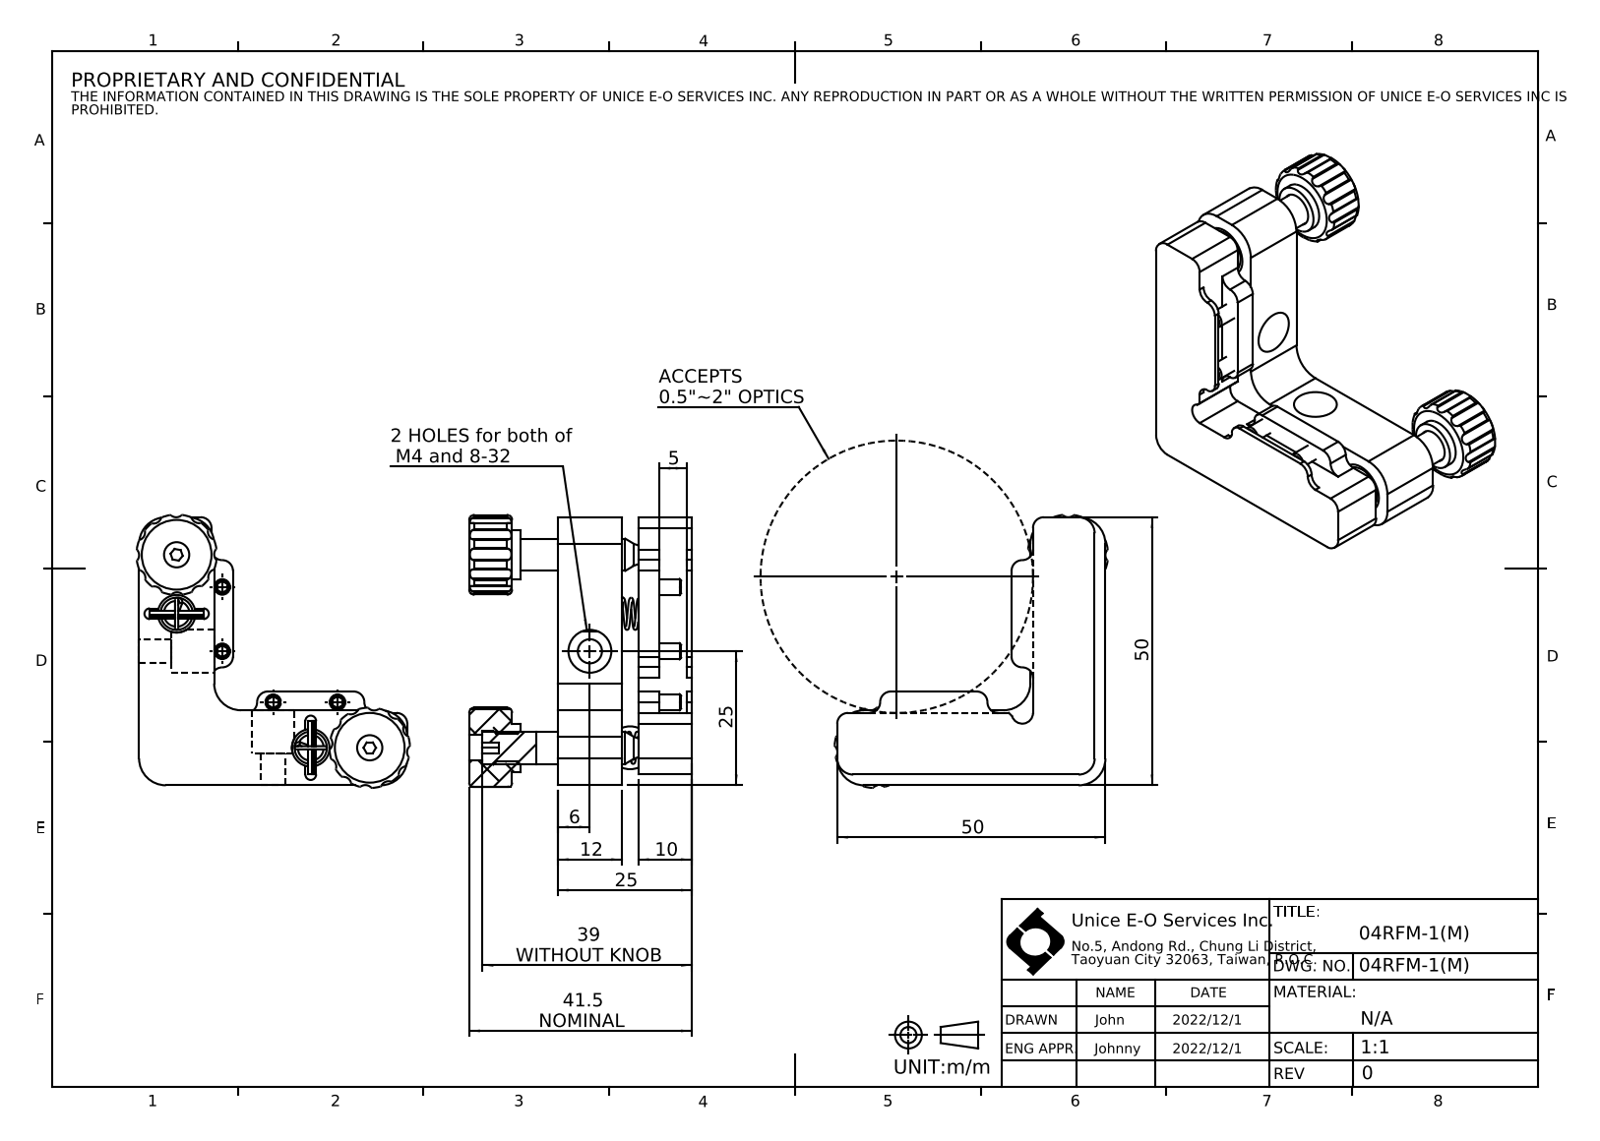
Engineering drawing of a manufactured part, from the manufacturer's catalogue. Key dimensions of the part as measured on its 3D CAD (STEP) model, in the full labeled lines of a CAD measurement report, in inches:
Part name (STEP PRODUCT): 04RFM-1(M)
STEP written by: SolidWorks 2021 (CONFIG_CONTROL_DESIGN)
Units: inches
Bodies: 0 solids, 329 faces (86 planar, 199 cylindrical, 44 other)
Overall size (bounding box): 2.004 × 2.004 × 1.634
Round holes (diameter × count): ⌀0.098 ×4, ⌀0.047 ×2, ⌀0.079 ×2, ⌀0.177 ×2, ⌀0.185 ×2, ⌀0.276 ×2, ⌀0.315 ×2, ⌀0.374 ×2, ⌀0.236 ×1
Round bosses / shafts (diameter × count): ⌀0.118 ×4, ⌀0.354 ×2, ⌀0.063 ×2, ⌀0.059 ×2, ⌀0.236 ×1
Partial cylindrical surfaces — rounded edges, fillets, slot ends (radius × count): R0.012 ×48, R0.059 ×24, R0.079 ×11, R0.197 ×6, R0.039 ×4, R0.118 ×3, R0.03 ×2, R0.295 ×2
Main face-to-face distances: 0.472, 0.984, 0.512, 0.118, 0.591, 0.394, 0.079, 0.551, 0.531, 0.453
Hole centre spacings: 0.388, 0.409, 0.433, 0.433, 0.472, 0.616, 0.72, 0.784
